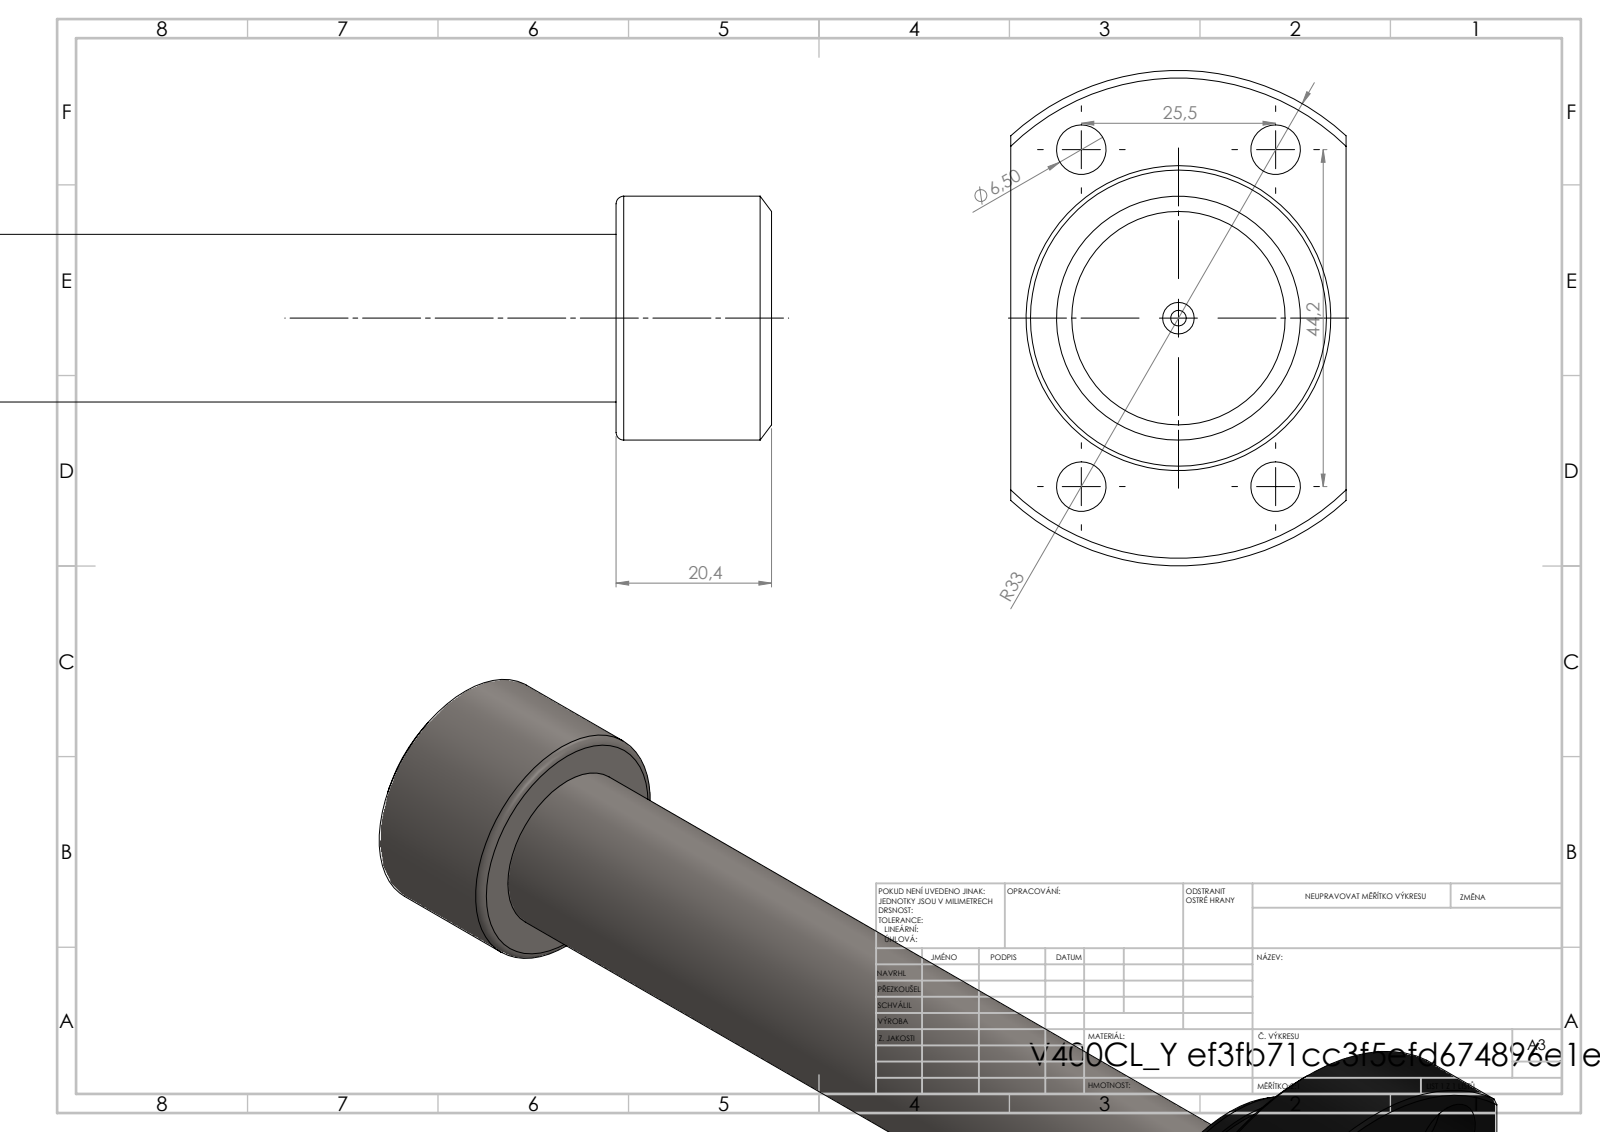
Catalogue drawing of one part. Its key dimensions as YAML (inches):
part_name: "V400CL_PC_Y; V400CL_VC_X"
step_written_by: "SolidWorks 2019 (CONFIG_CONTROL_DESIGN)"
units: inches
bodies: {solids: 2, faces: 103, planar: 26, cylindrical: 47, other: 30}
overall_size: [6.969, 2.559, 1.732]
volume: 6.982
surface_area: 41.46
round_holes:
  - {diameter: 0.256, count: 4}
  - {diameter: 0.413, count: 4}
  - {diameter: 0.081, count: 1}
  - {diameter: 0.197, count: 1}
  - {diameter: 0.236, count: 1}
  - {diameter: 0.866, count: 1}
  - {diameter: 1.043, count: 1}
round_bosses_or_shafts:
  - {diameter: 1.575, count: 1}
  - {diameter: 1.535, count: 1}
  - {diameter: 1.26, count: 1}
partial_cylinders:
  - {radius: 0.423, count: 1}
  - {radius: 1.28, count: 1}
face_to_face_distances: [0.551, 0.531, 1.083, 1.732, 5.648, 6.179, 6.73, 0.803, 4.844, 5.376]
hole_center_spacings: [1.004, 1.004, 1.74, 2.009]
